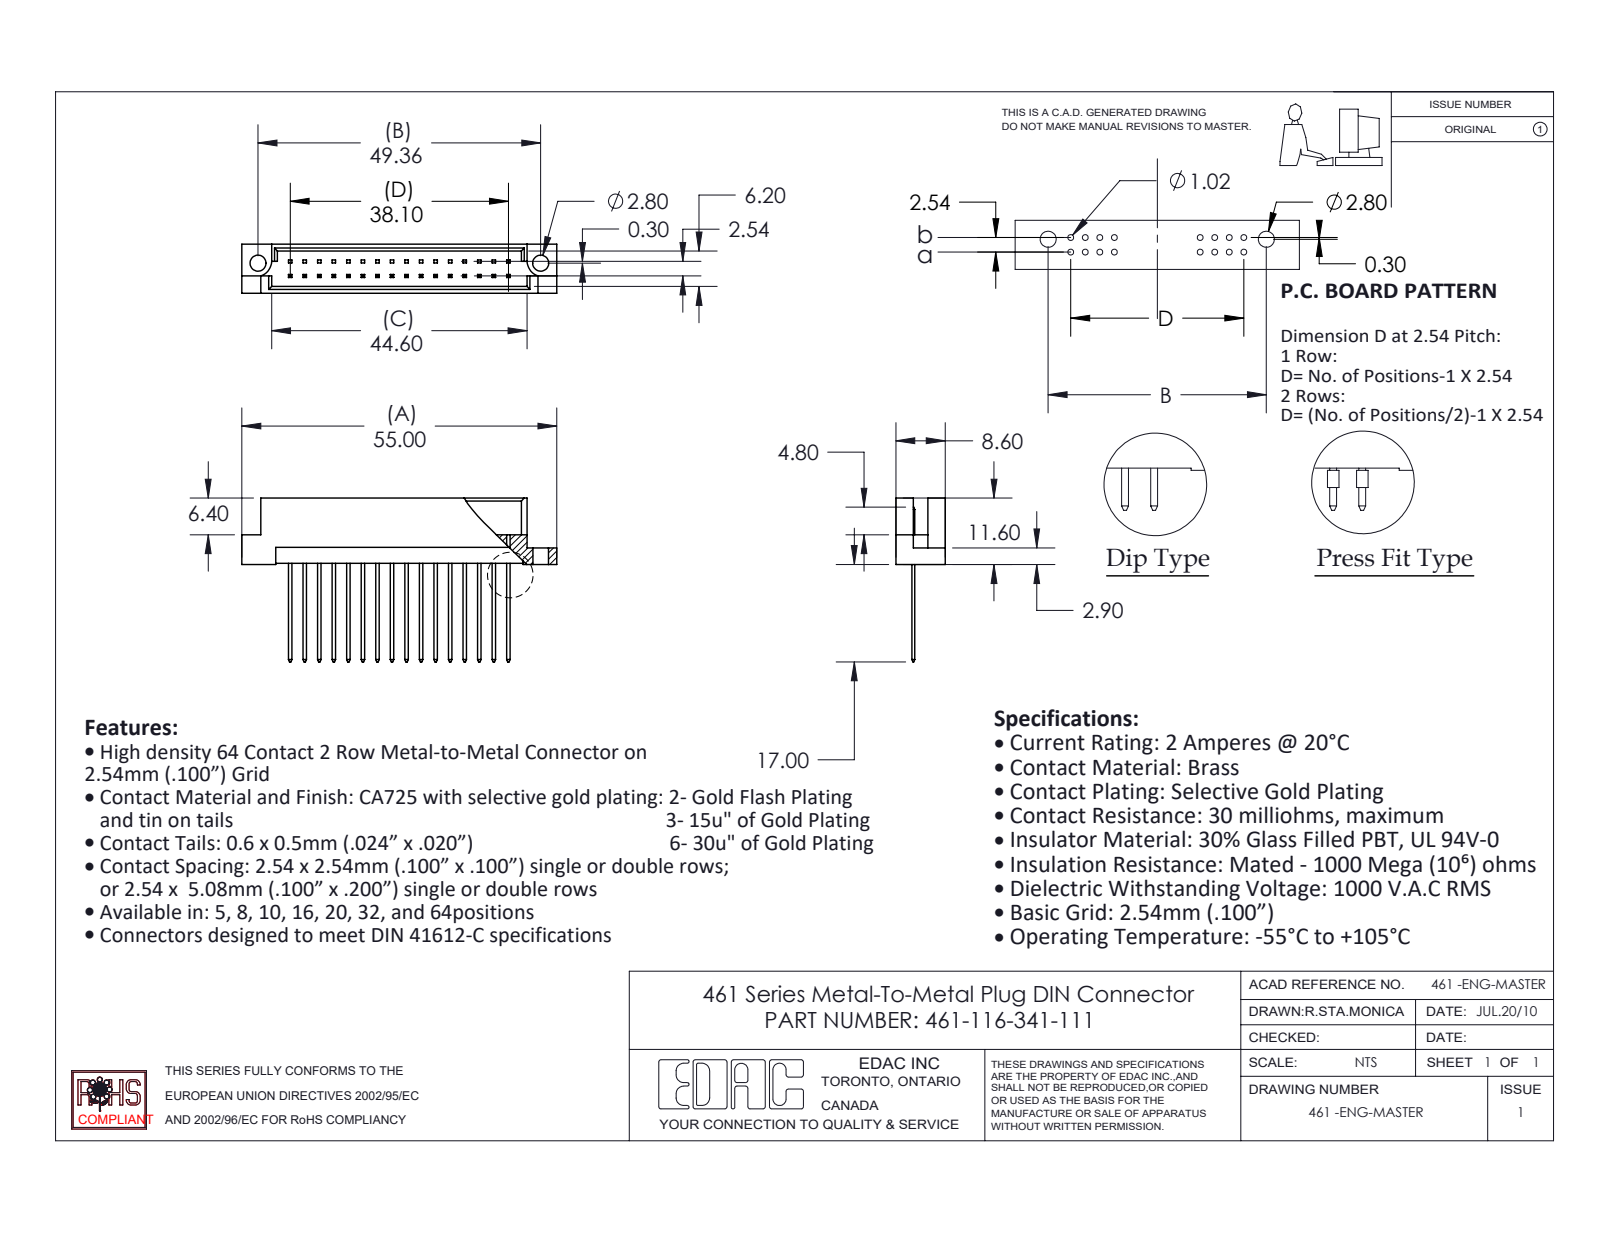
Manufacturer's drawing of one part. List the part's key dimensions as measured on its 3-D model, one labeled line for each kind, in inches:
Part name (STEP PRODUCT): 461-116-341-111; 461-290_41; 461 Part_32
STEP written by: SolidWorks 2020 (CONFIG_CONTROL_DESIGN)
Units: inches
Bodies: 17 solids, 400 faces (394 planar, 6 cylindrical, 0 other)
Overall size (bounding box): 2.165 × 1.126 × 0.339
Volume: 0.17 in³ · Surface area: 6.498 in²
Round holes (diameter × count): ⌀0.11 ×2
Partial cylindrical surfaces — rounded edges, fillets, slot ends (radius × count): R0.11 ×2
Main face-to-face distances: 0.047, 0.291, 0.339, 0.244, 0.109, 0.229, 0.062, 0.182, 0.129, 0.209
Hole centre spacings: 1.943
